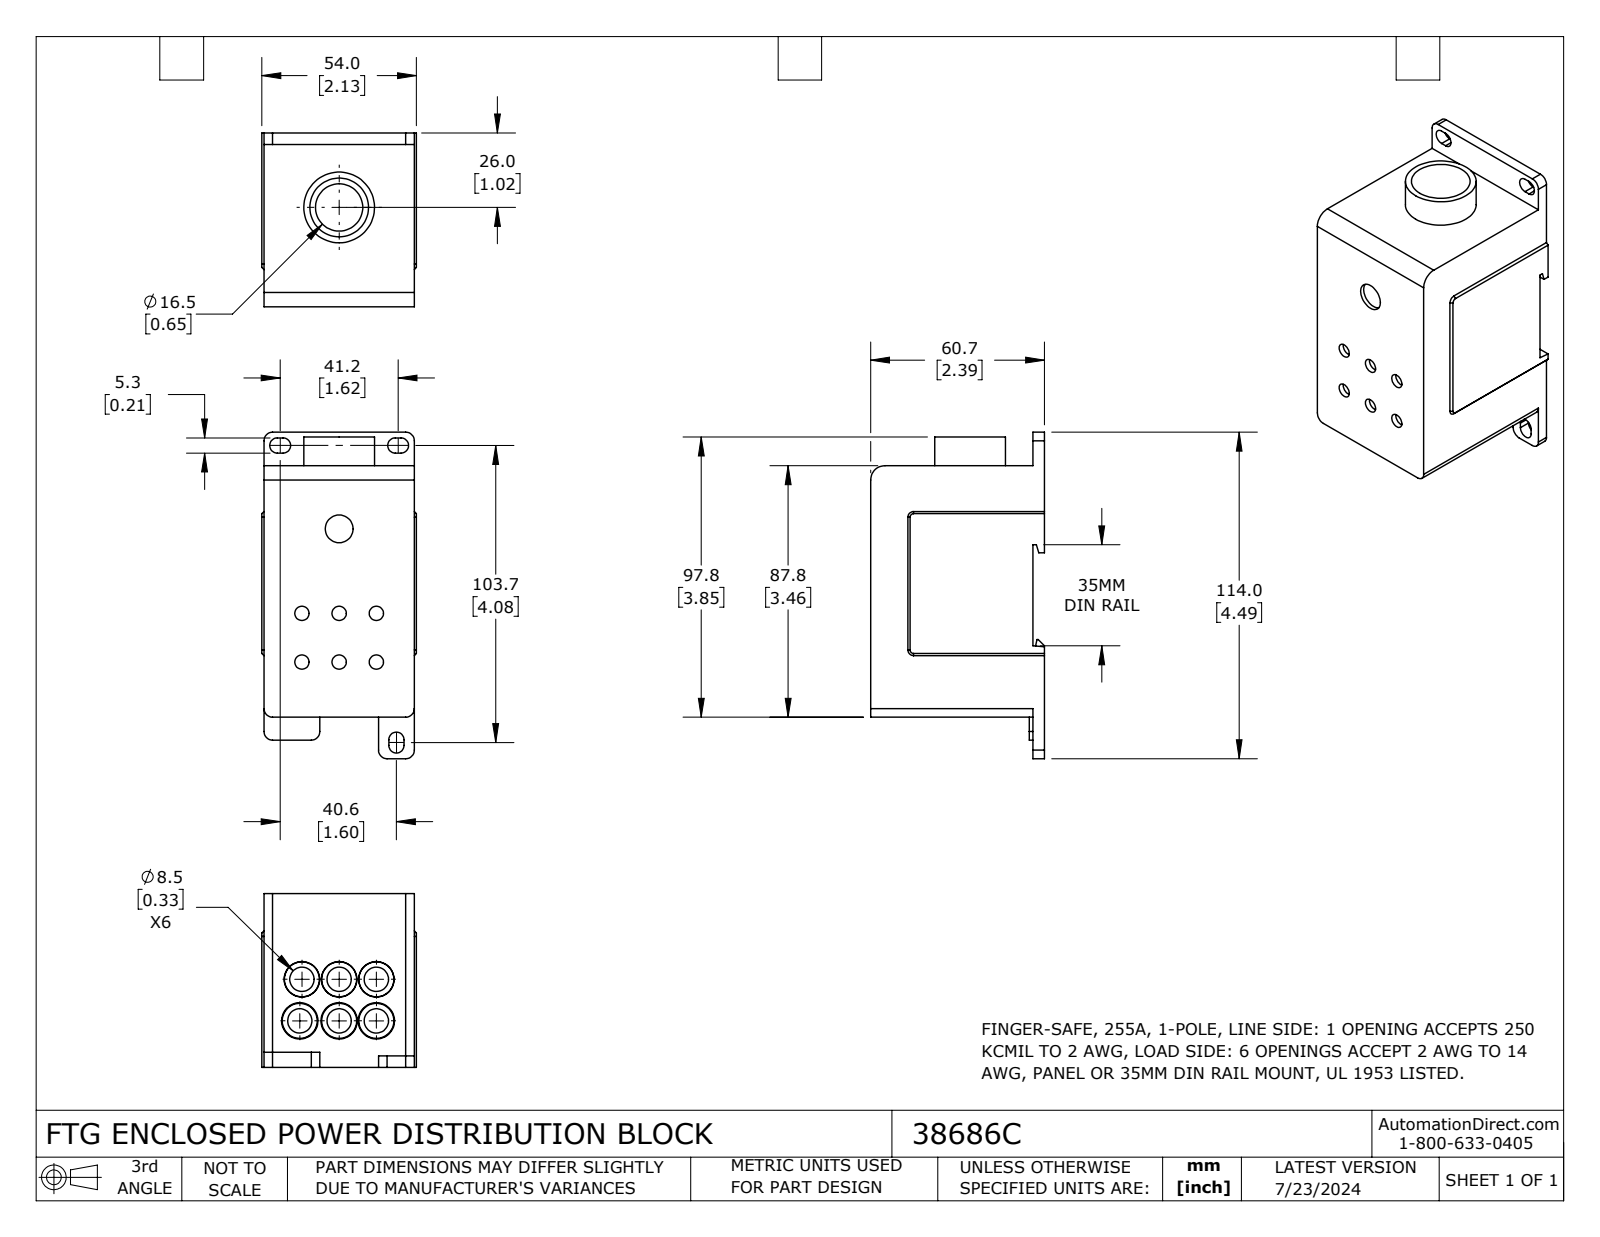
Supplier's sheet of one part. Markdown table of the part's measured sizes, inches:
| quantity | value |
| --- | --- |
| part name | 38686C |
| STEP written by | SolidWorks 2023 (CONFIG_CONTROL_DESIGN) |
| units | inches |
| bodies | 1 solid, 139 faces (46 planar, 49 cylindrical, 44 other) |
| overall size | 4.488 × 2.39 × 2.126 |
| volume | 15.39 in³ |
| surface area | 60.88 in² |
| round holes (diameter × count) | 0.197 × 6, 0.335 × 6, 0.382 × 1, 0.65 × 1, 0.807 × 1 |
| round bosses / shafts (diameter × count) | 0.972 × 1 |
| partial cylindrical surfaces (radius × count) | 0.118 × 8, 0.104 × 6, 0.197 × 1 |
| main face-to-face distances | 0.03, 2.096, 2.39, 2.067, 0.157, 2.232, 2.126, 3.457, 3.917, 0.461 |
| hole center spacings | 0.512, 0.843, 0.669, 0.767, 1.024, 0.545, 0.571, 1.223 |
